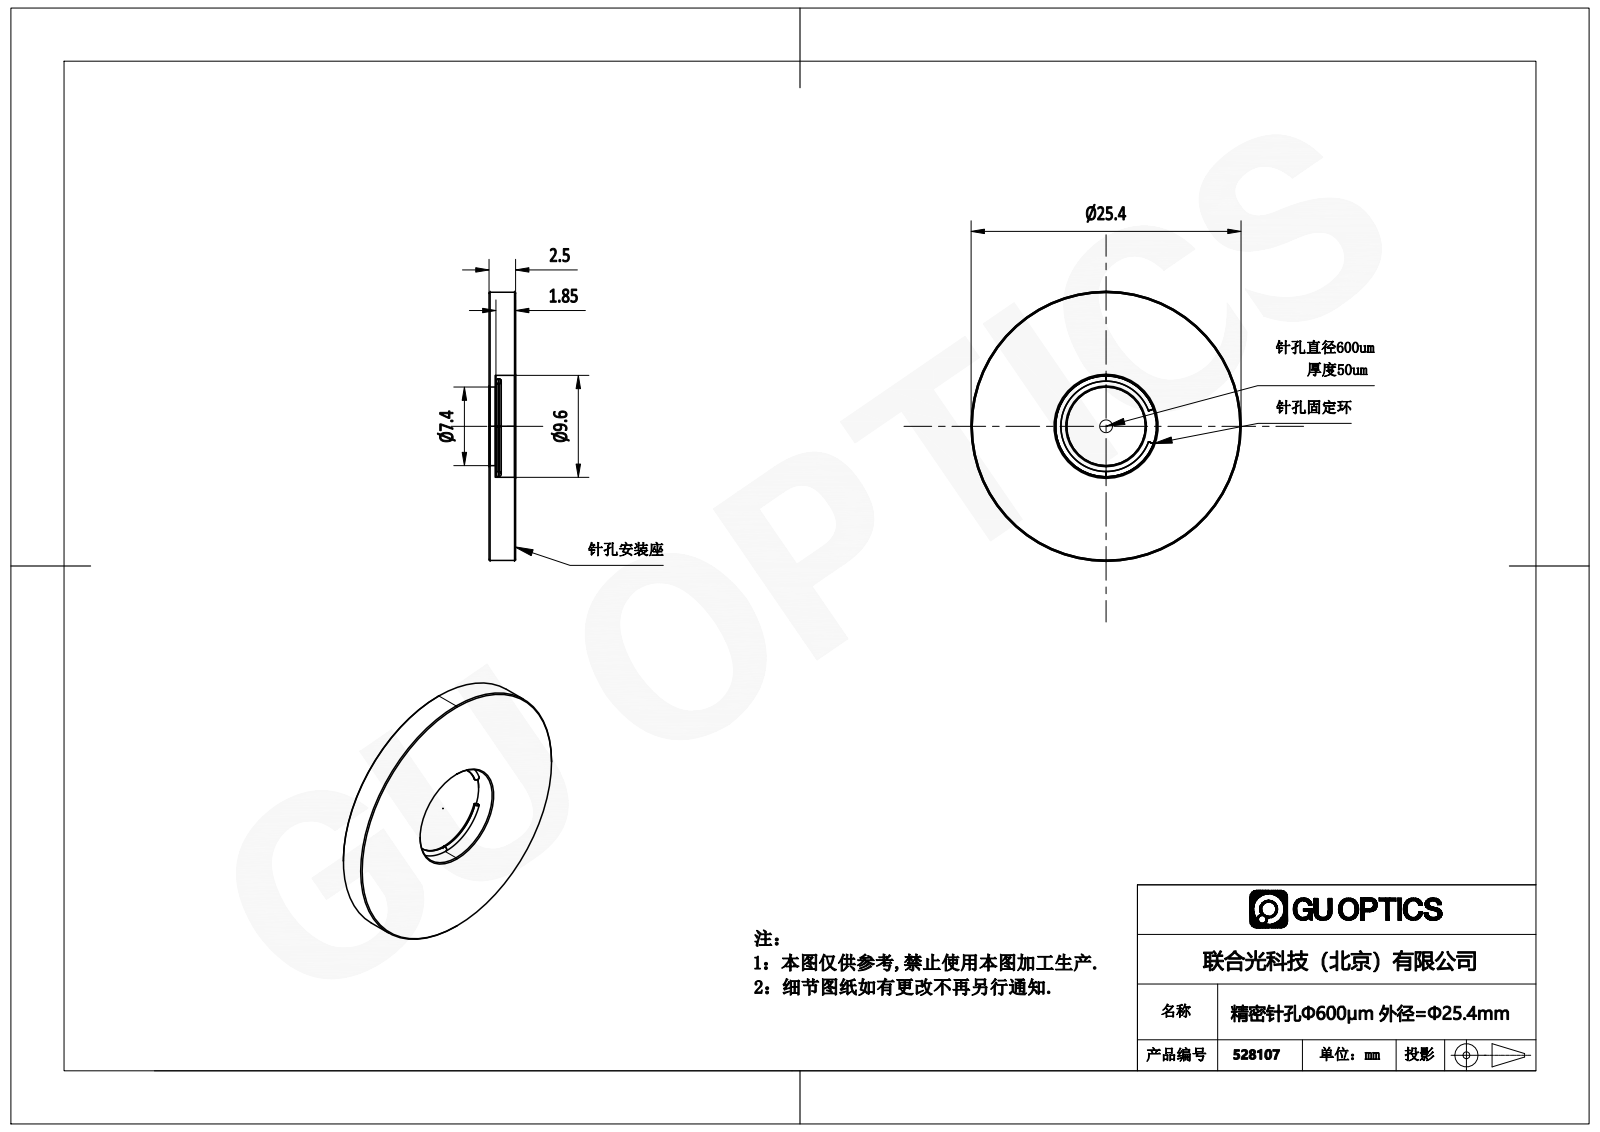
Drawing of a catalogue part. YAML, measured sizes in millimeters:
part_name: "1.5.3.36_ZXO-1.0-600_精密针孔600um，直径25.4（1.0英寸）"
step_written_by: "SolidWorks 2018 (CONFIG_CONTROL_DESIGN)"
units: millimeters
bodies: {solids: 0, faces: 28, planar: 6, cylindrical: 8, other: 14}
overall_size: [25.4, 25.4, 2.5]
round_holes:
  - {diameter: 0.6, count: 1}
  - {diameter: 7.4, count: 1}
  - {diameter: 9.6, count: 1}
round_bosses_or_shafts:
  - {diameter: 25.4, count: 1}
face_to_face_distances: [2.5, 0.6, 0.65, 1.9, 1.85]
